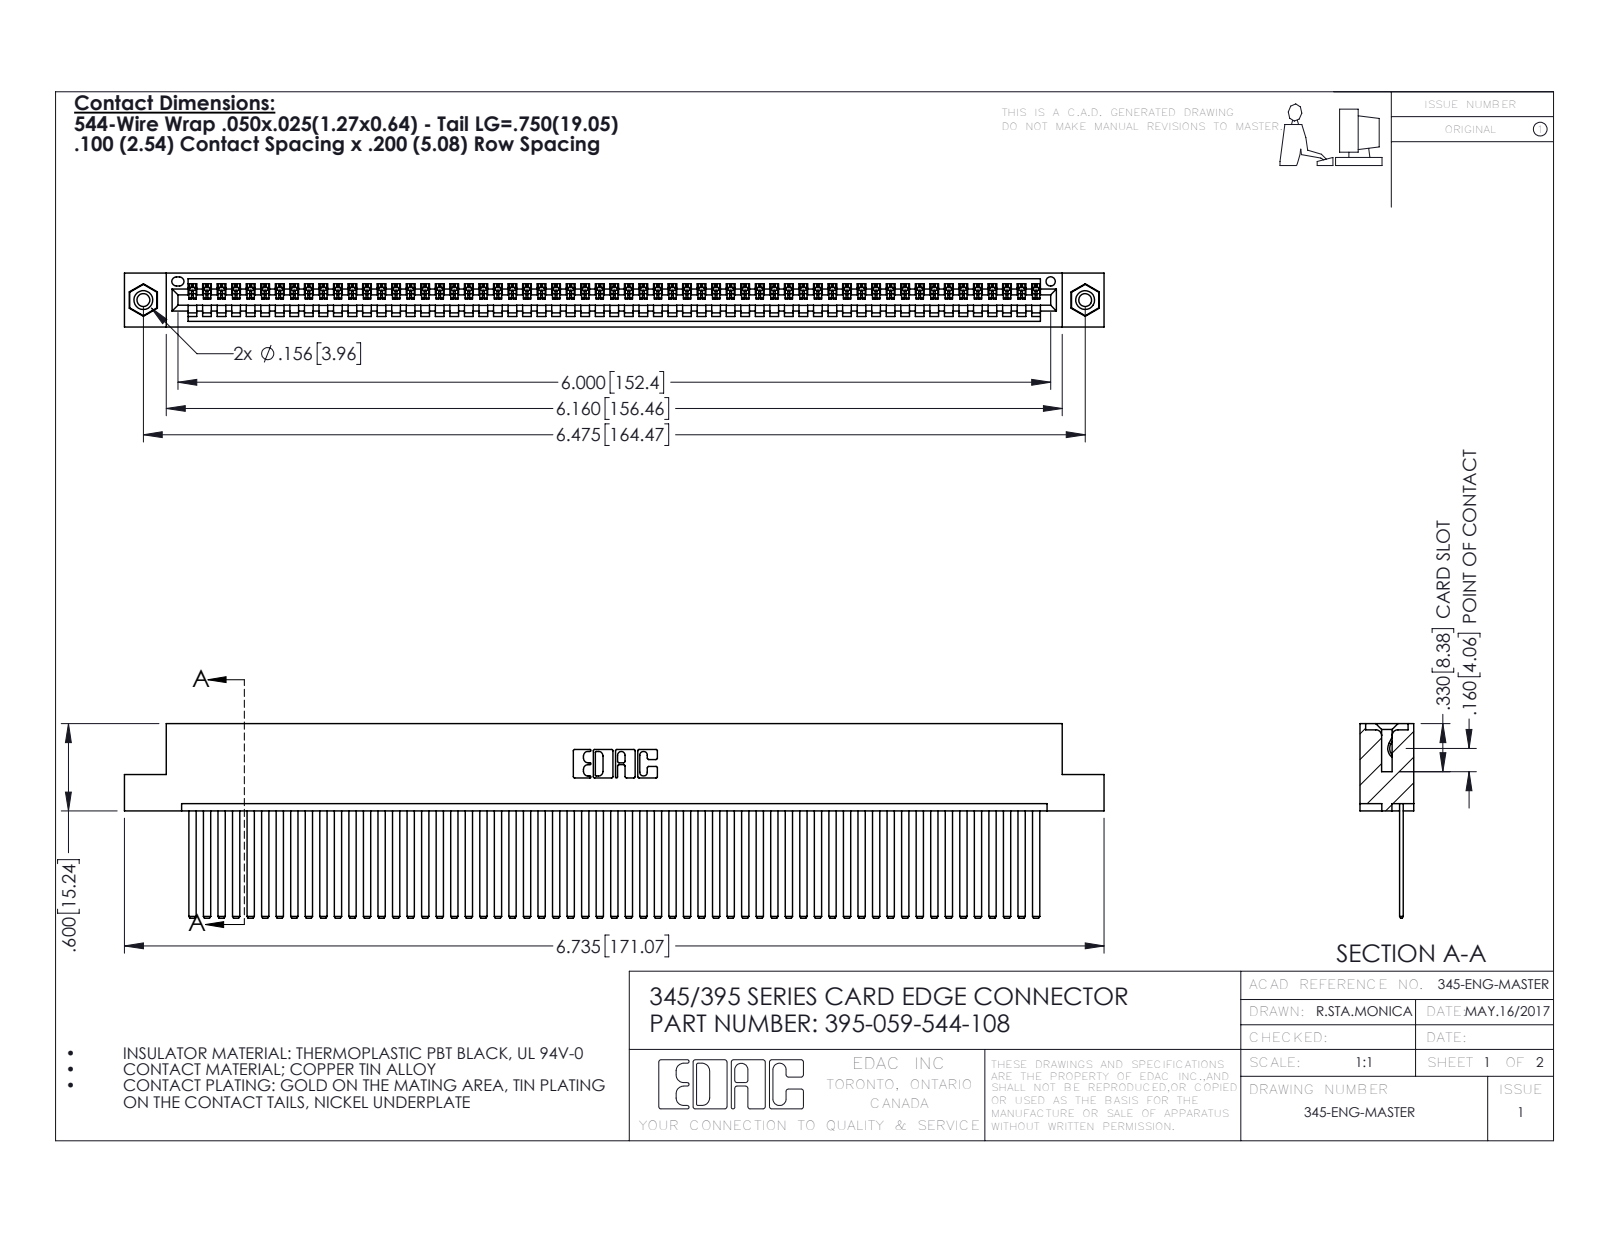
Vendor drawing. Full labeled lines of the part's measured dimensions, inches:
Part name (STEP PRODUCT): 395-059-544-108; 345-292-001_345-293-144; 345 Part_Flush Mounting Lugs - 0.156 Dia-TI; 345-250-001_345-250-003-102
STEP written by: SolidWorks 2016 (CONFIG_CONTROL_DESIGN)
Units: inches
Bodies: 62 solids, 3254 faces (2236 planar, 1002 cylindrical, 16 other)
Overall size (bounding box): 6.735 × 1.337 × 0.37
Volume: 1.041 in³ · Surface area: 38.72 in²
Round holes (diameter × count): ⌀0.089 ×2, ⌀0.125 ×2, ⌀0.156 ×2, ⌀0.064 ×1
Round bosses / shafts (diameter × count): ⌀0.155 ×2
Partial cylindrical surfaces — rounded edges, fillets, slot ends (radius × count): R0.006 ×118, R0.01 ×22, R0.007 ×6, R0.031 ×6, R0.026 ×3, R0.031 ×2, R0.04 ×2, R0.014 ×1
Main face-to-face distances: 0.072, 0.298, 0.025, 0.098, 0.272, 0.37, 0.2, 0.225, 0.149, 0.072
Hole centre spacings: 0.27, 6.239, 6.475
